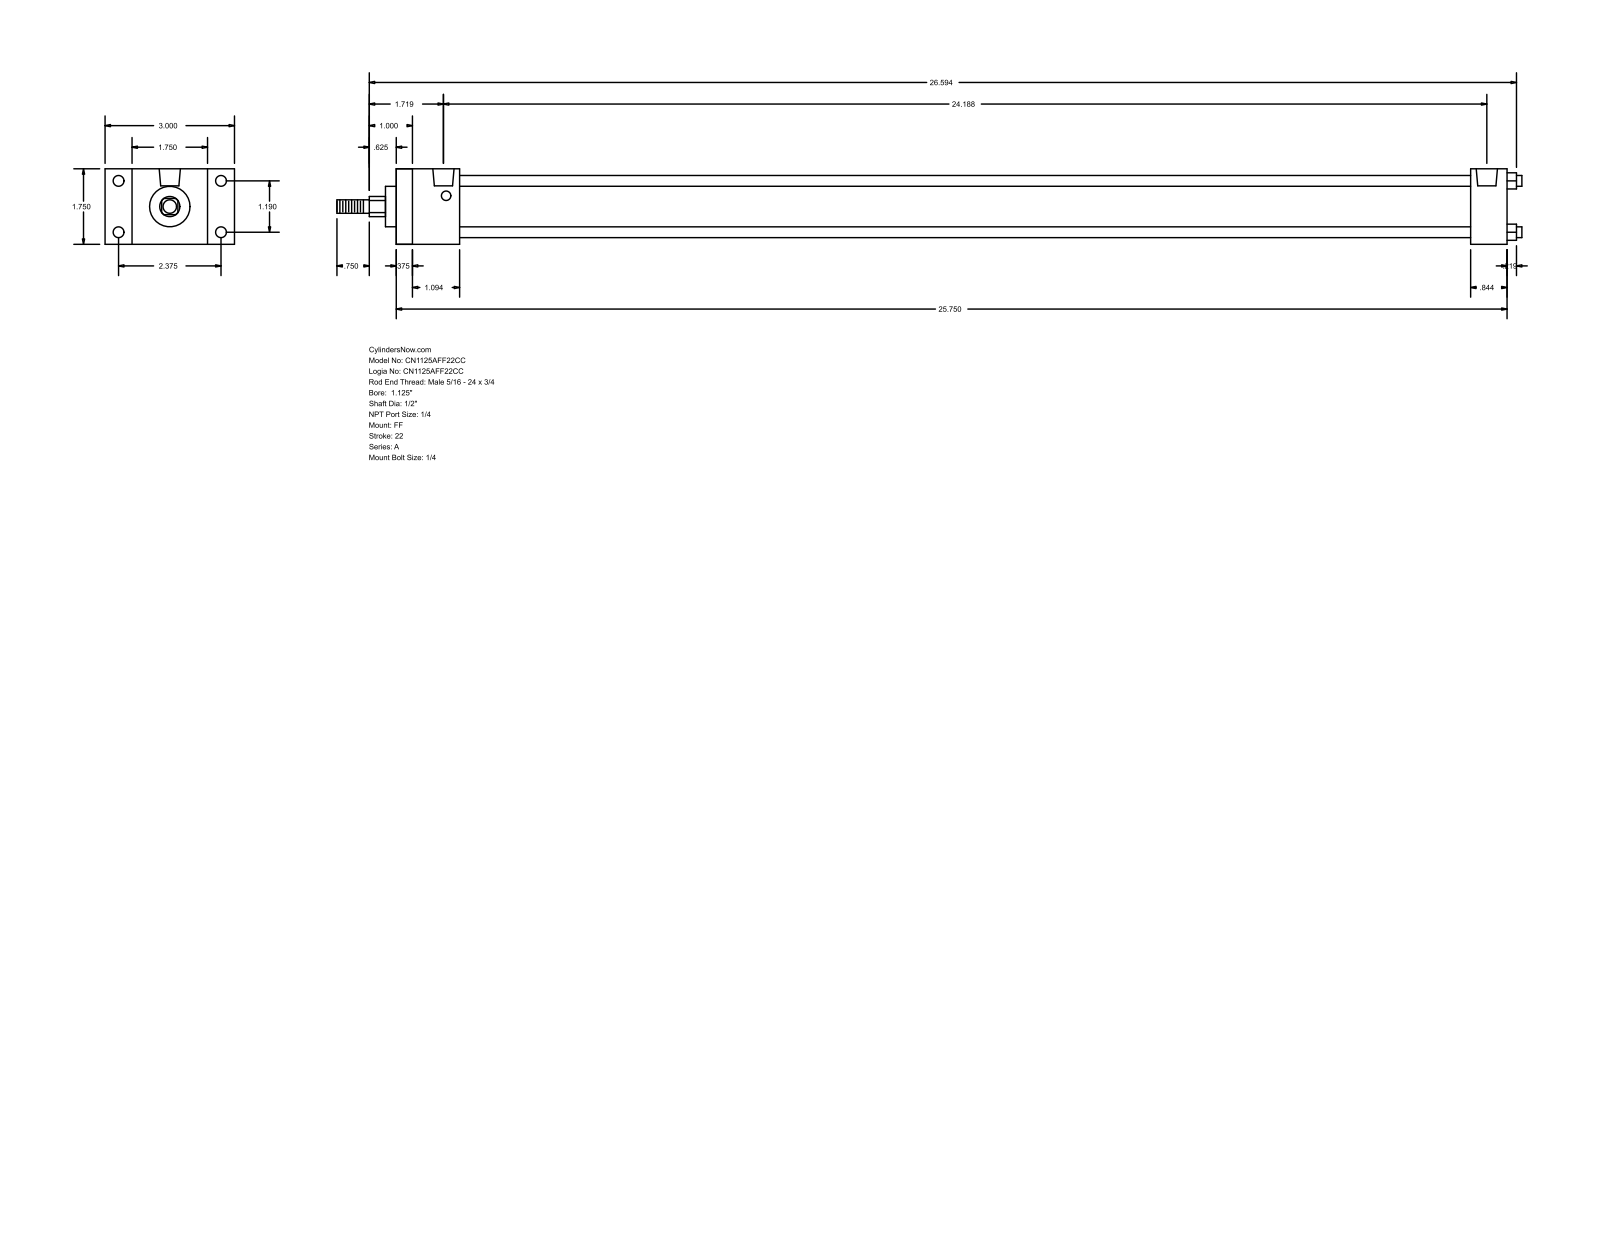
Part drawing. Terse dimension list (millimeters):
name: A_FF__0112_0.5
written by: GSSL Pune (CONFIG_CONTROL_DESIGN)
unit: mm
bodies: 0 solids, 92 faces (64 planar, 28 cylindrical, 0 other)
size: 697.71 × 76.2 × 44.45
holes: 4× ⌀5.56, 4× ⌀6.35, 2× ⌀12.49
bosses: 4× ⌀6.35, 1× ⌀31.88, 1× ⌀23.81, 1× ⌀12.7, 1× ⌀7.94
rounds: 1× R5.94
face distances: 44.46, 654.04, 9.52, 644.52, 15.87, 632.61, 623.09, 21.43, 37.3, 27.78
hole spacings: 30.22, 60.32, 67.47, 611.19, 1.58, 1.59, 612.77, 612.78
